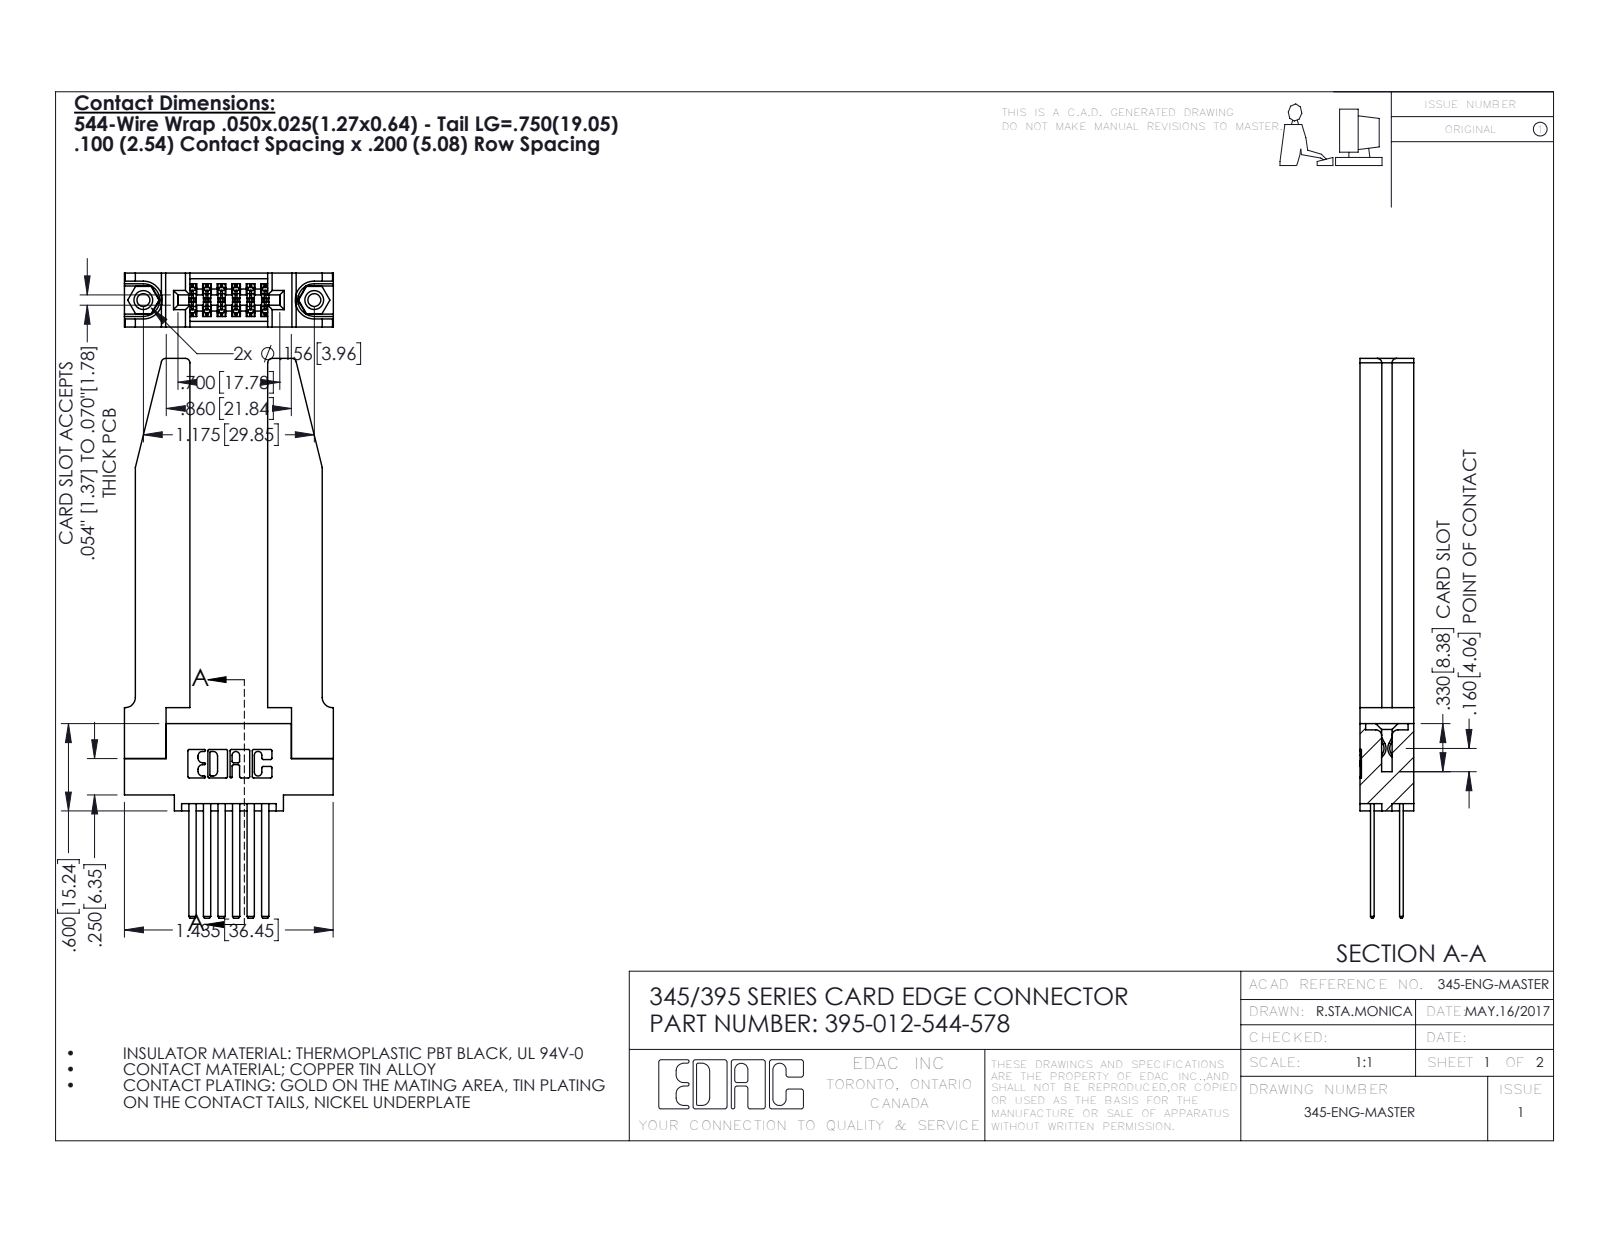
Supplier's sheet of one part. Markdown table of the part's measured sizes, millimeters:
| quantity | value |
| --- | --- |
| part name | 345-292-001_345-293-144; 395-012-544-578; 345 Part_0.110 Offset - 0.156 Dia-TH; 345-250-001_345-250-001-102 (+1 more) |
| STEP written by | SolidWorks 2016 (CONFIG_CONTROL_DESIGN) |
| units | millimeters |
| bodies | 17 solids, 892 faces (574 planar, 266 cylindrical, 52 other) |
| overall size | 97.7 × 36.5 × 9.4 |
| volume | 11 100 mm³ |
| surface area | 11 610 mm² |
| round holes (diameter × count) | 2.3 × 2, 3.2 × 2, 4 × 2, 1.6 × 1 |
| round bosses / shafts (diameter × count) | 3.9 × 2 |
| partial cylindrical surfaces (radius × count) | 0.3 × 22, 0.2 × 18, 0.8 × 8, 0.2 × 6, 0.8 × 6, 0.7 × 3, 0.4 × 2, 0.5 × 2 |
| main face-to-face distances | 9.4, 1.8, 7.6, 3.8, 3.8, 5.1, 5.6, 2, 2.5, 6.9 |
| hole center spacings | 6.9, 24, 29.8 |
